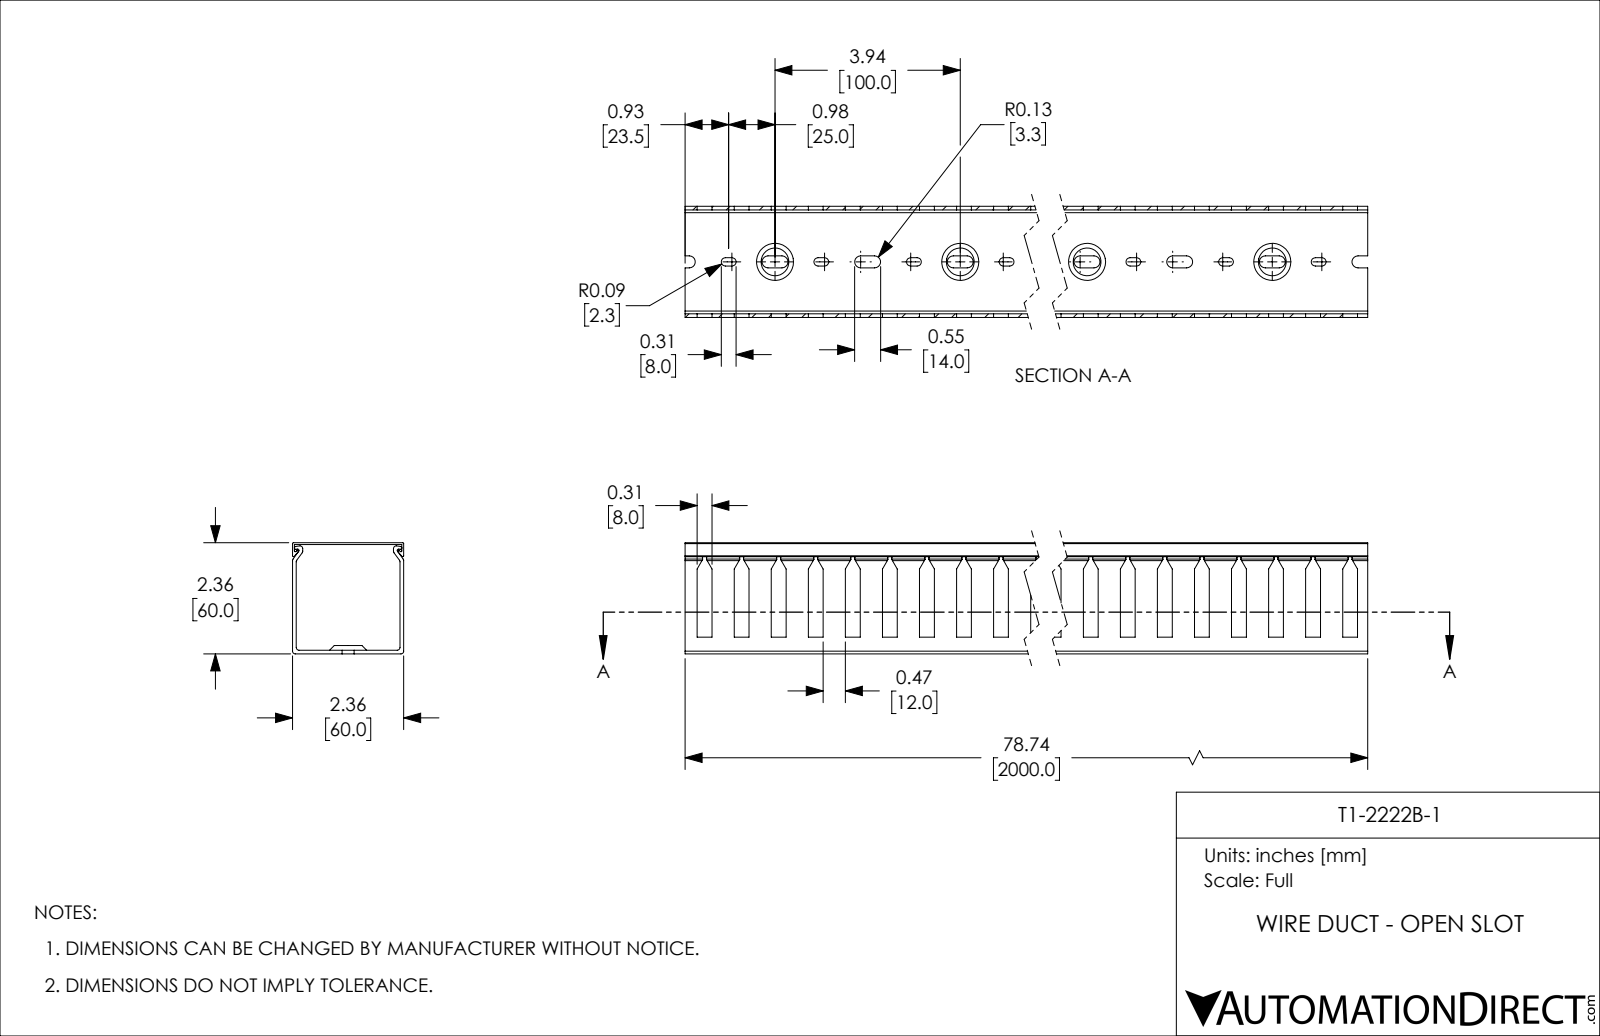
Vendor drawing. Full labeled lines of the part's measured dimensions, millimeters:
Part name (STEP PRODUCT): T1-2222B-1
STEP written by: SolidWorks 2021 (CONFIG_CONTROL_DESIGN)
Units: millimetres
Bodies: 2 solids, 1005 faces (534 planar, 431 cylindrical, 40 other)
Overall size (bounding box): 2000 × 60 × 60
Volume: 854 712 mm³ · Surface area: 1 012 000 mm²
Partial cylindrical surfaces — rounded edges, fillets, slot ends (radius × count): R2.25 ×80, R3.25 ×80, R1.5 ×12, R0.5 ×8, R0.75 ×6
Main face-to-face distances: 2, 58, 60, 1, 59, 57, 56, 4.5, 54.5, 5.5
